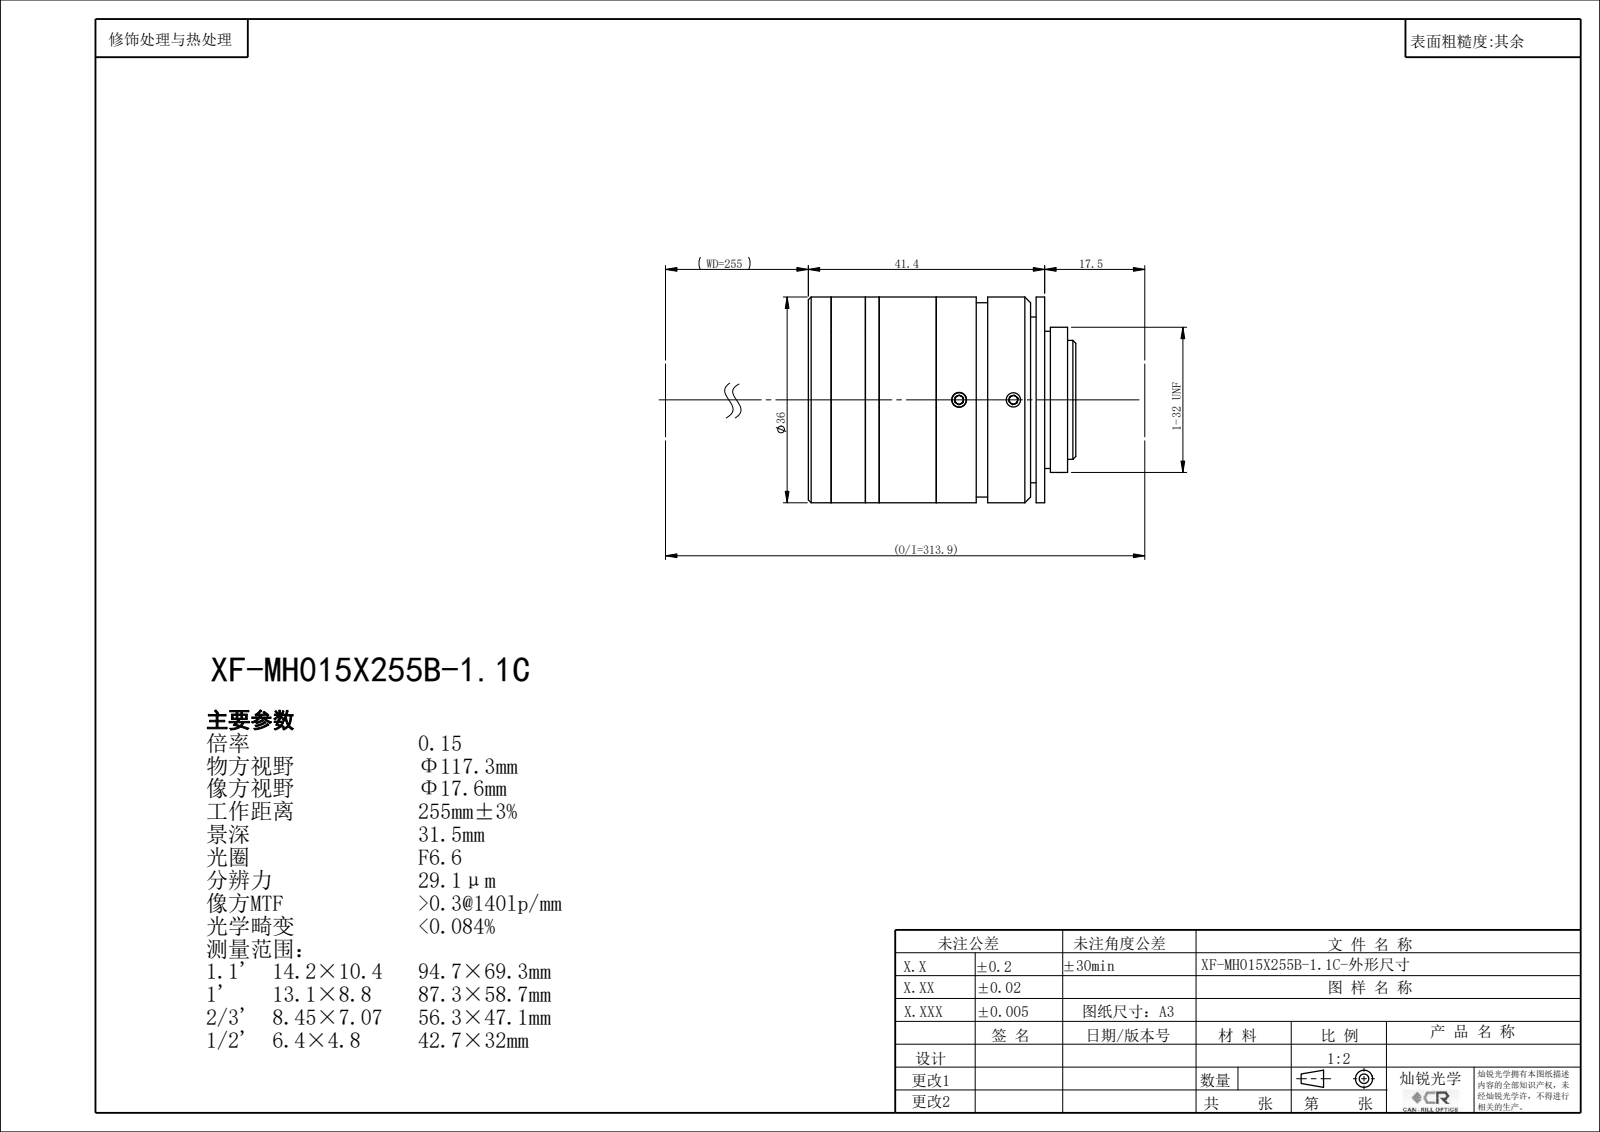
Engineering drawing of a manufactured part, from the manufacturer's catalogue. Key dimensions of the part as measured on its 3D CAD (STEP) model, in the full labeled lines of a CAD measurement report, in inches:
Part name (STEP PRODUCT): XF-MH015X255B-1.1C
STEP written by: SolidWorks 2022 (CONFIG_CONTROL_DESIGN)
Units: inches
Bodies: 0 solids, 154 faces (78 planar, 44 cylindrical, 32 other)
Overall size (bounding box): 1.843 × 1.417 × 1.417
Round holes (diameter × count): ⌀0.098 ×3, ⌀0.551 ×1, ⌀0.646 ×1, ⌀0.669 ×1, ⌀0.724 ×1, ⌀0.882 ×1, ⌀0.945 ×1, ⌀0.98 ×1, ⌀1.024 ×1
Round bosses / shafts (diameter × count): ⌀1.417 ×1, ⌀1.339 ×1, ⌀1 ×1, ⌀0.819 ×1
Main face-to-face distances: 0.747, 1.629, 0.882, 0.059, 1.57, 0.688, 0.394, 0.488, 1.393, 1.082
